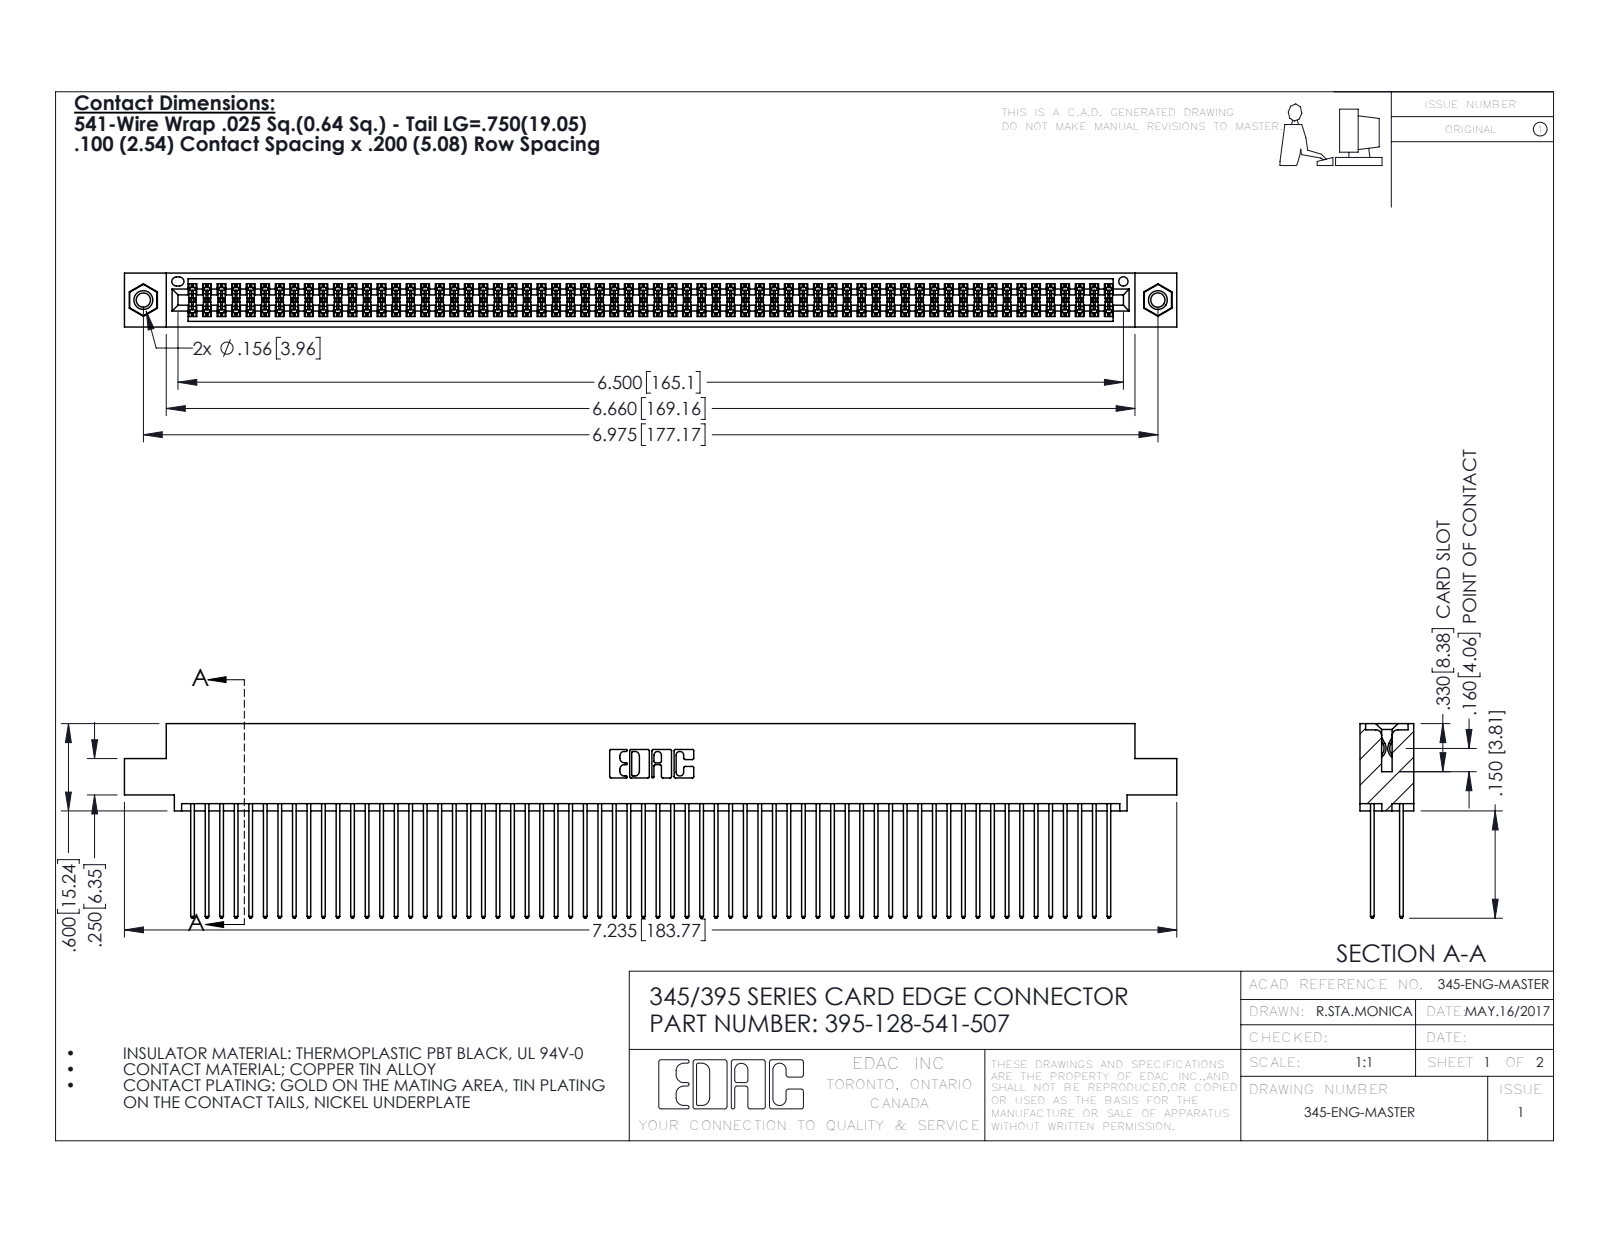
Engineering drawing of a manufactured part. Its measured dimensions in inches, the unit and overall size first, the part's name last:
Units: inches
Overall size (bounding box): 7.235 × 1.337 × 0.37
Round holes (diameter × count): ⌀0.098 ×2, ⌀0.125 ×2, ⌀0.156 ×2, ⌀0.064 ×1
Round bosses / shafts (diameter × count): ⌀0.155 ×2
Partial cylindrical surfaces — rounded edges, fillets, slot ends (radius × count): R0.006 ×192, R0.01 ×128, R0.01 ×22, R0.007 ×6, R0.031 ×6, R0.026 ×3, R0.014 ×2, R0.019 ×2
Main face-to-face distances: 0.072, 0.298, 0.2, 0.098, 0.272, 0.025, 0.225, 0.37, 0.175, 0.149
Hole centre spacings: 0.27, 6.739, 6.975
Volume: 1.141 in³ · Surface area: 49.05 in²
Bodies: 131 solids, 6590 faces (4340 planar, 2234 cylindrical, 16 other)
Part name (STEP PRODUCT): 395-128-541-507; 345-292-001_345-293-141; 345-250-001_345-250-005-103; 345 Part_0.110 Offset - 0.156 Dia-TI
STEP written by: SolidWorks 2016 (CONFIG_CONTROL_DESIGN)
